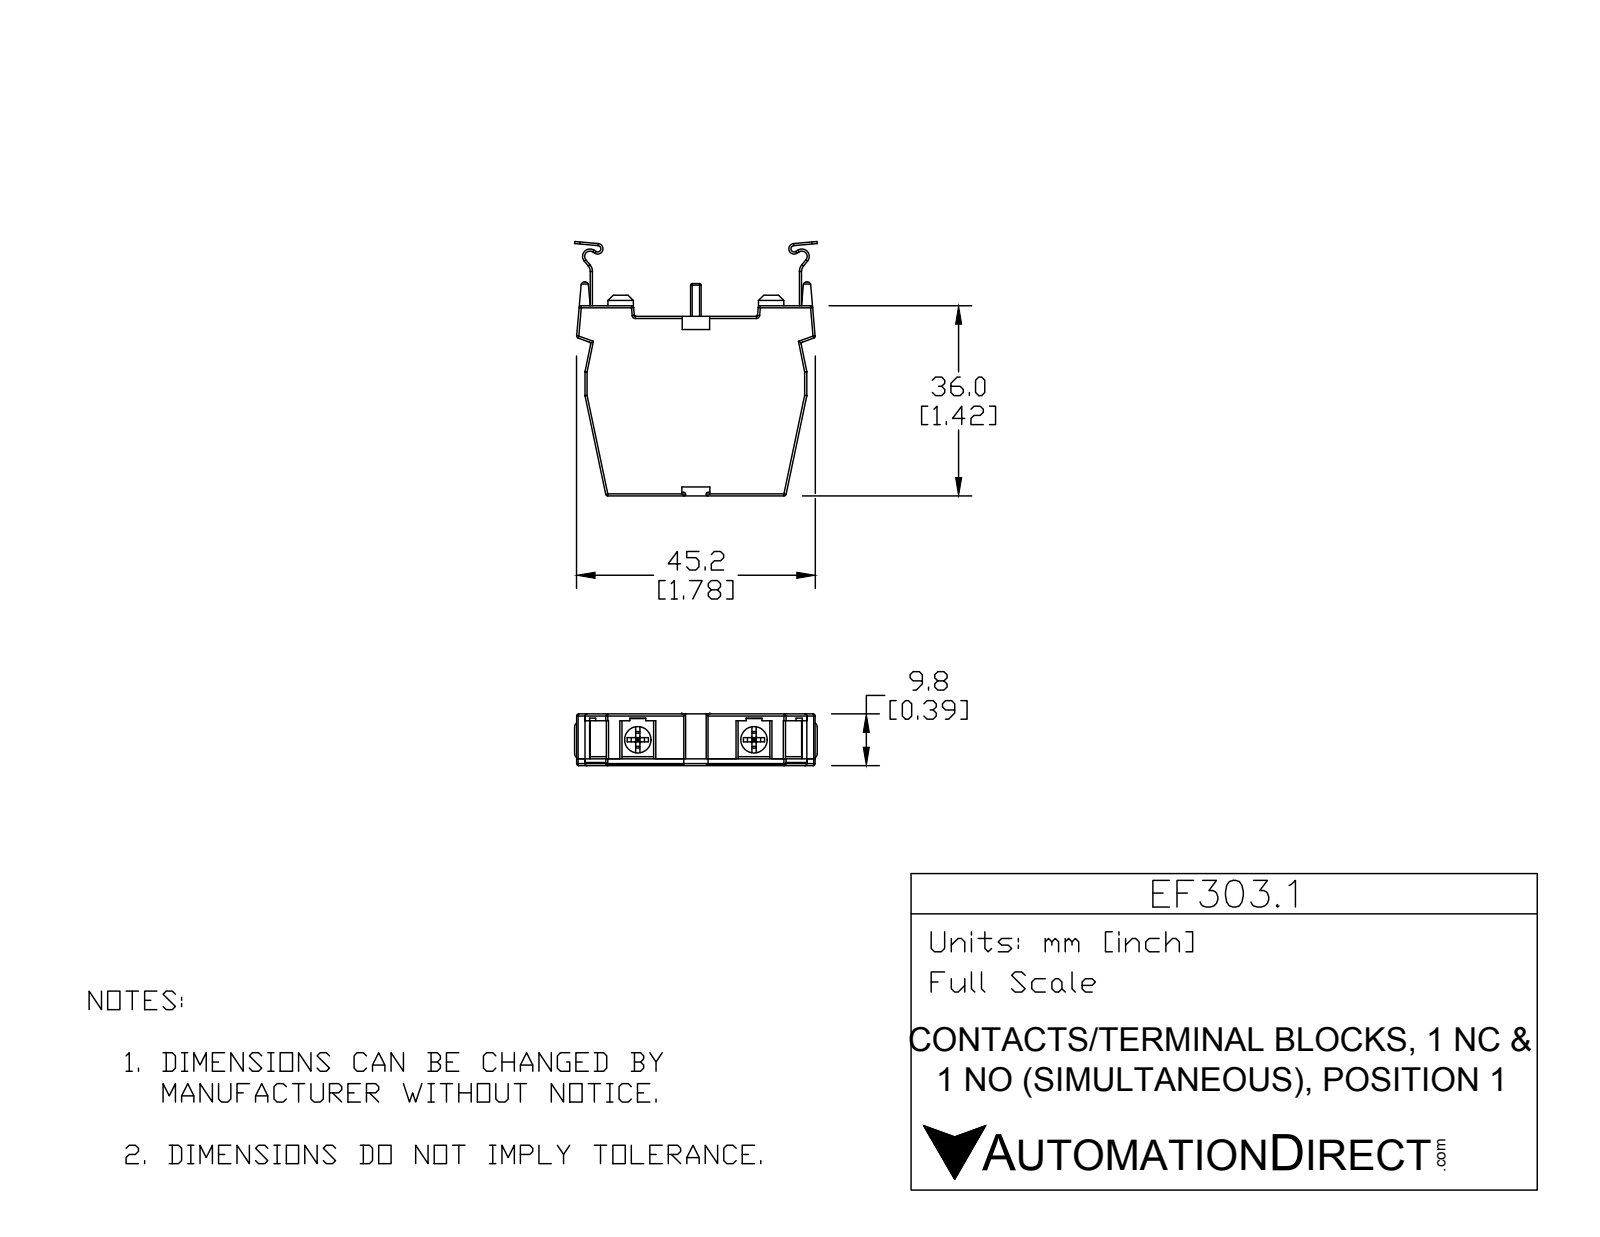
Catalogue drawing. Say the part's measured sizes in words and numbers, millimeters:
The part is named "EF303.1". Its 3-D file was written by "SolidWorks 2015 (AUTOMOTIVE_DESIGN)". It is 7 solids with 299 faces: 173 planar, 104 cylindrical and 22 other. Overall it measures 48.16 by 46.28 by 9.8 millimeters. Its volume is 12 135 cubic millimeters and its surface area 6 604 square millimeters. Round holes: 4 of diameter 5. Round bosses or shafts: 4 of diameter 4, 2 of diameter 4.75. Partial cylindrical surfaces (rounded edges, fillets, slot ends): 44 of radius 0.25, 8 of radius 0.5, 6 of radius 1, 4 of radius 0.6, 2 of radius 0.6, 2 of radius 1, 2 of radius 1.4, 2 of radius 1.6. The main face-to-face distances are 9.8, 1.4, 8.4, 34, 7, 2, 0.4, 3.18, 37.18, 36. The hole center spacings are 21.81.
